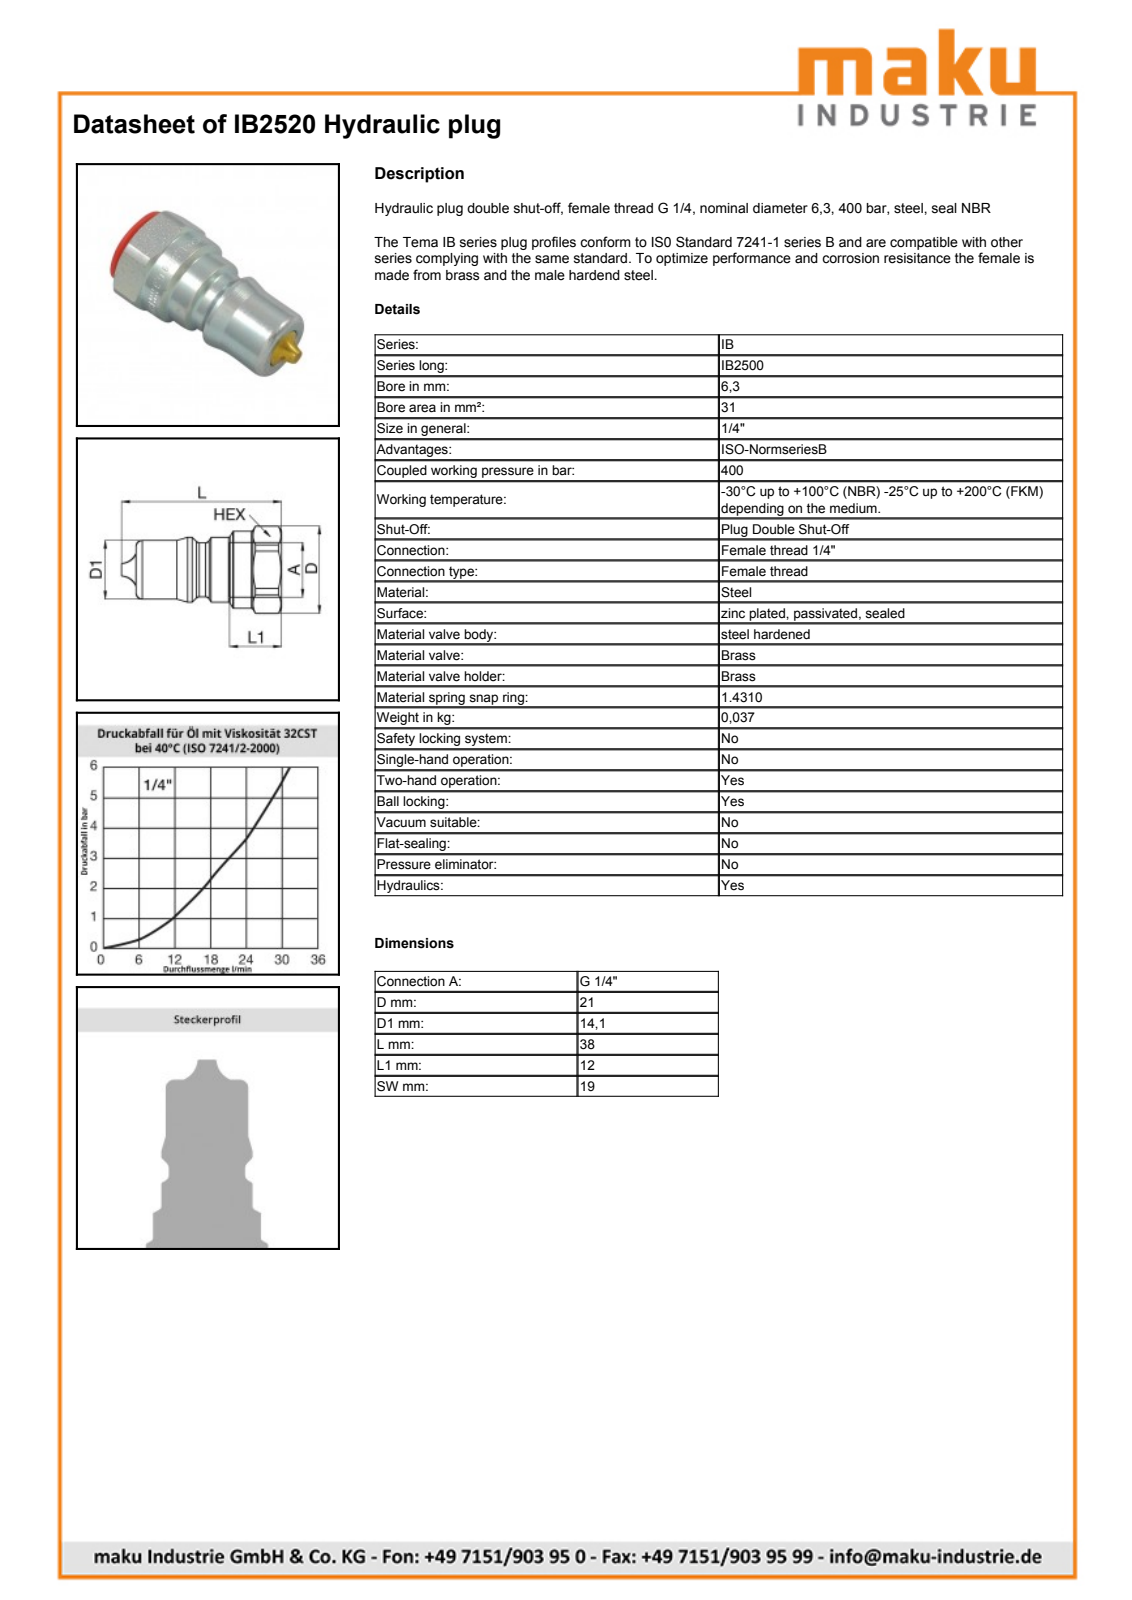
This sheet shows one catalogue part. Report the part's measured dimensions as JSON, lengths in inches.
{"part_name": "IB2520", "step_written_by": "SolidWorks 2009 (AUTOMOTIVE_DESIGN)", "units": "inches", "bodies": {"solids": 1, "faces": 63, "planar": 10, "cylindrical": 21, "other": 32}, "overall_size": [1.515, 0.827, 0.748], "volume_in3": 0.379, "surface_area_in2": 4.245, "round_holes": [[0.315, 1], [0.45, 1]], "round_bosses_or_shafts": [[0.728, 1], [0.614, 1], [0.555, 1], [0.512, 1]], "partial_cylinders_radius": [[0.413, 1]], "face_to_face_distances": [0.748, 0.426, 1.378, 0.952, 1.515, 1.089, 0.137]}
